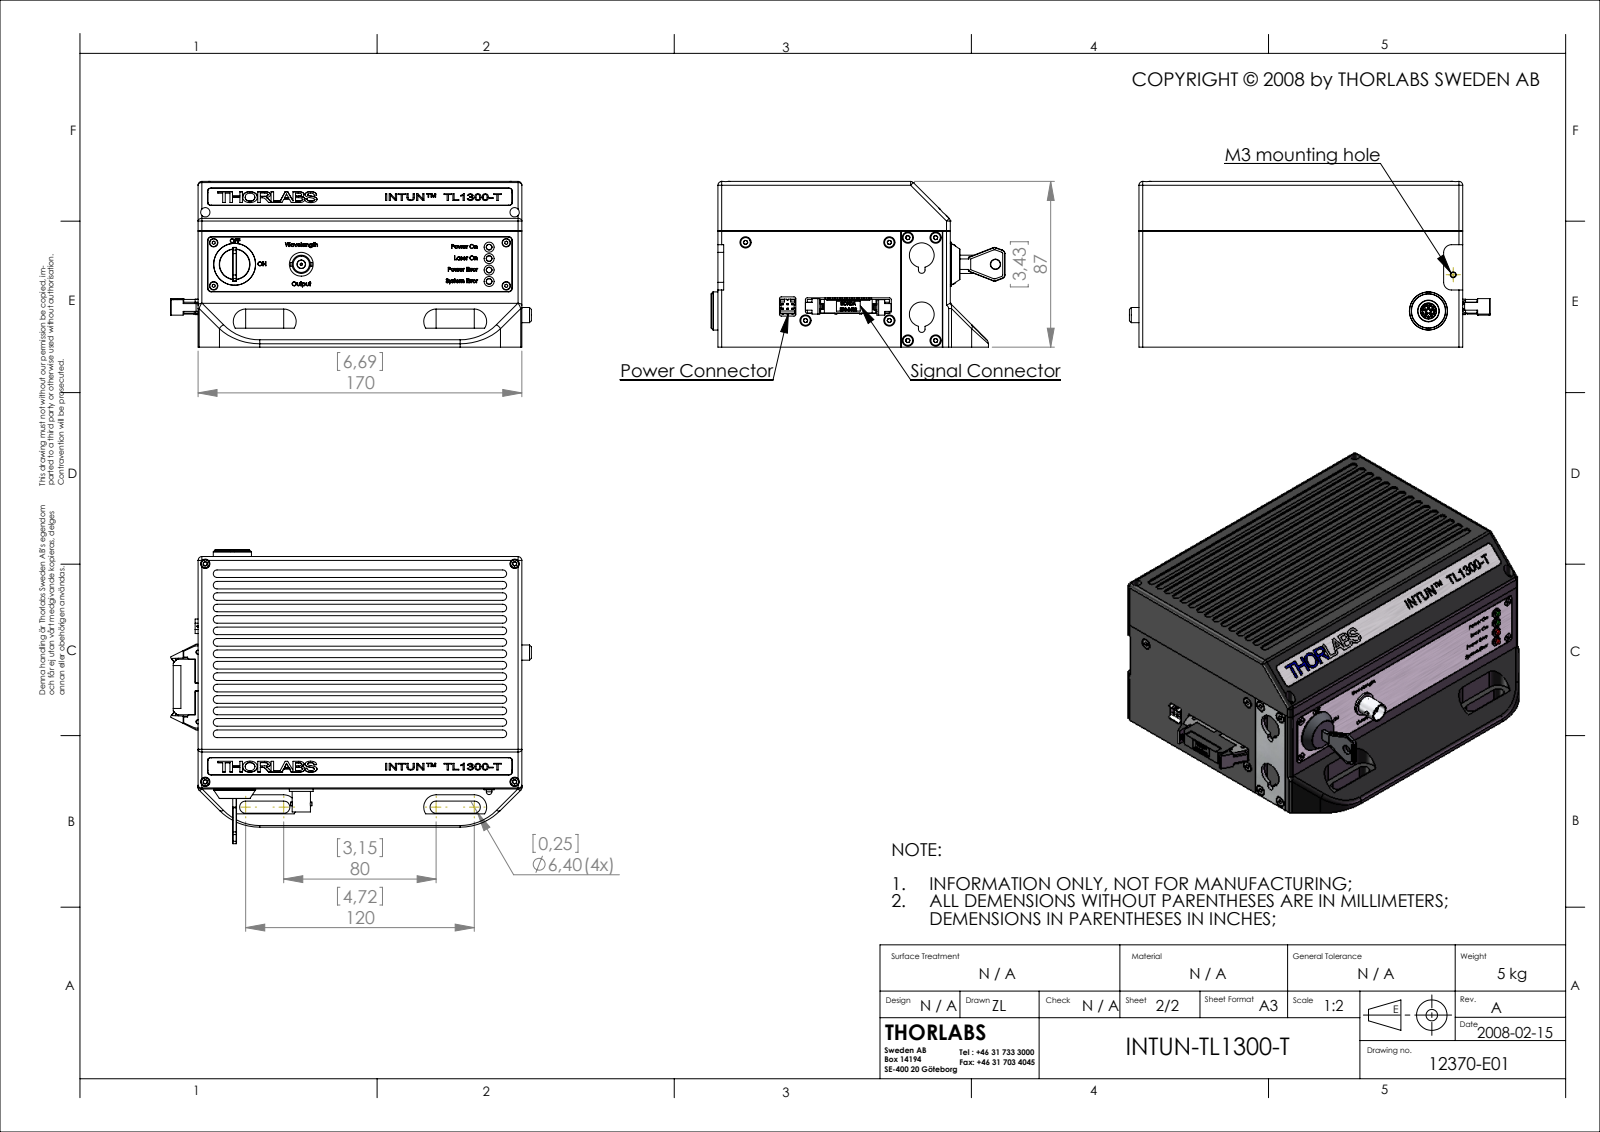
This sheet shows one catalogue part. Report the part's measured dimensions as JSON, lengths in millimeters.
{"part_name": "INTUN-TL1300-T", "step_written_by": "SolidWorks 2007 (CONFIG_CONTROL_DESIGN)", "units": "millimeters", "bodies": {"solids": 0, "faces": 7167, "planar": 4896, "cylindrical": 1137, "other": 1134}, "overall_size": [267, 154.2, 110.3], "round_holes": [[1, 33], [2.7, 17], [2.05, 13], [2.4, 12], [1.6, 8], [2.9, 8], [4.9, 8], [2.2, 6], [11, 6], [3, 5], [4.3, 5], [4.5, 5]], "round_bosses_or_shafts": [[2, 11], [4, 8], [5.7, 6], [5.3, 6], [3, 6], [2.5, 6], [22, 5], [6.2, 5]], "partial_cylinders_radius": [[2, 89], [5, 37], [0.15, 20], [0.99, 20], [1.8, 16], [0.2, 14], [1, 12], [6, 12]], "face_to_face_distances": [5, 1, 3, 6, 2, 6.25, 87, 86, 5.6, 84], "hole_center_spacings": [3.2, 3.46, 4.84, 6.34, 1.8, 5.82, 34.06, 44]}
